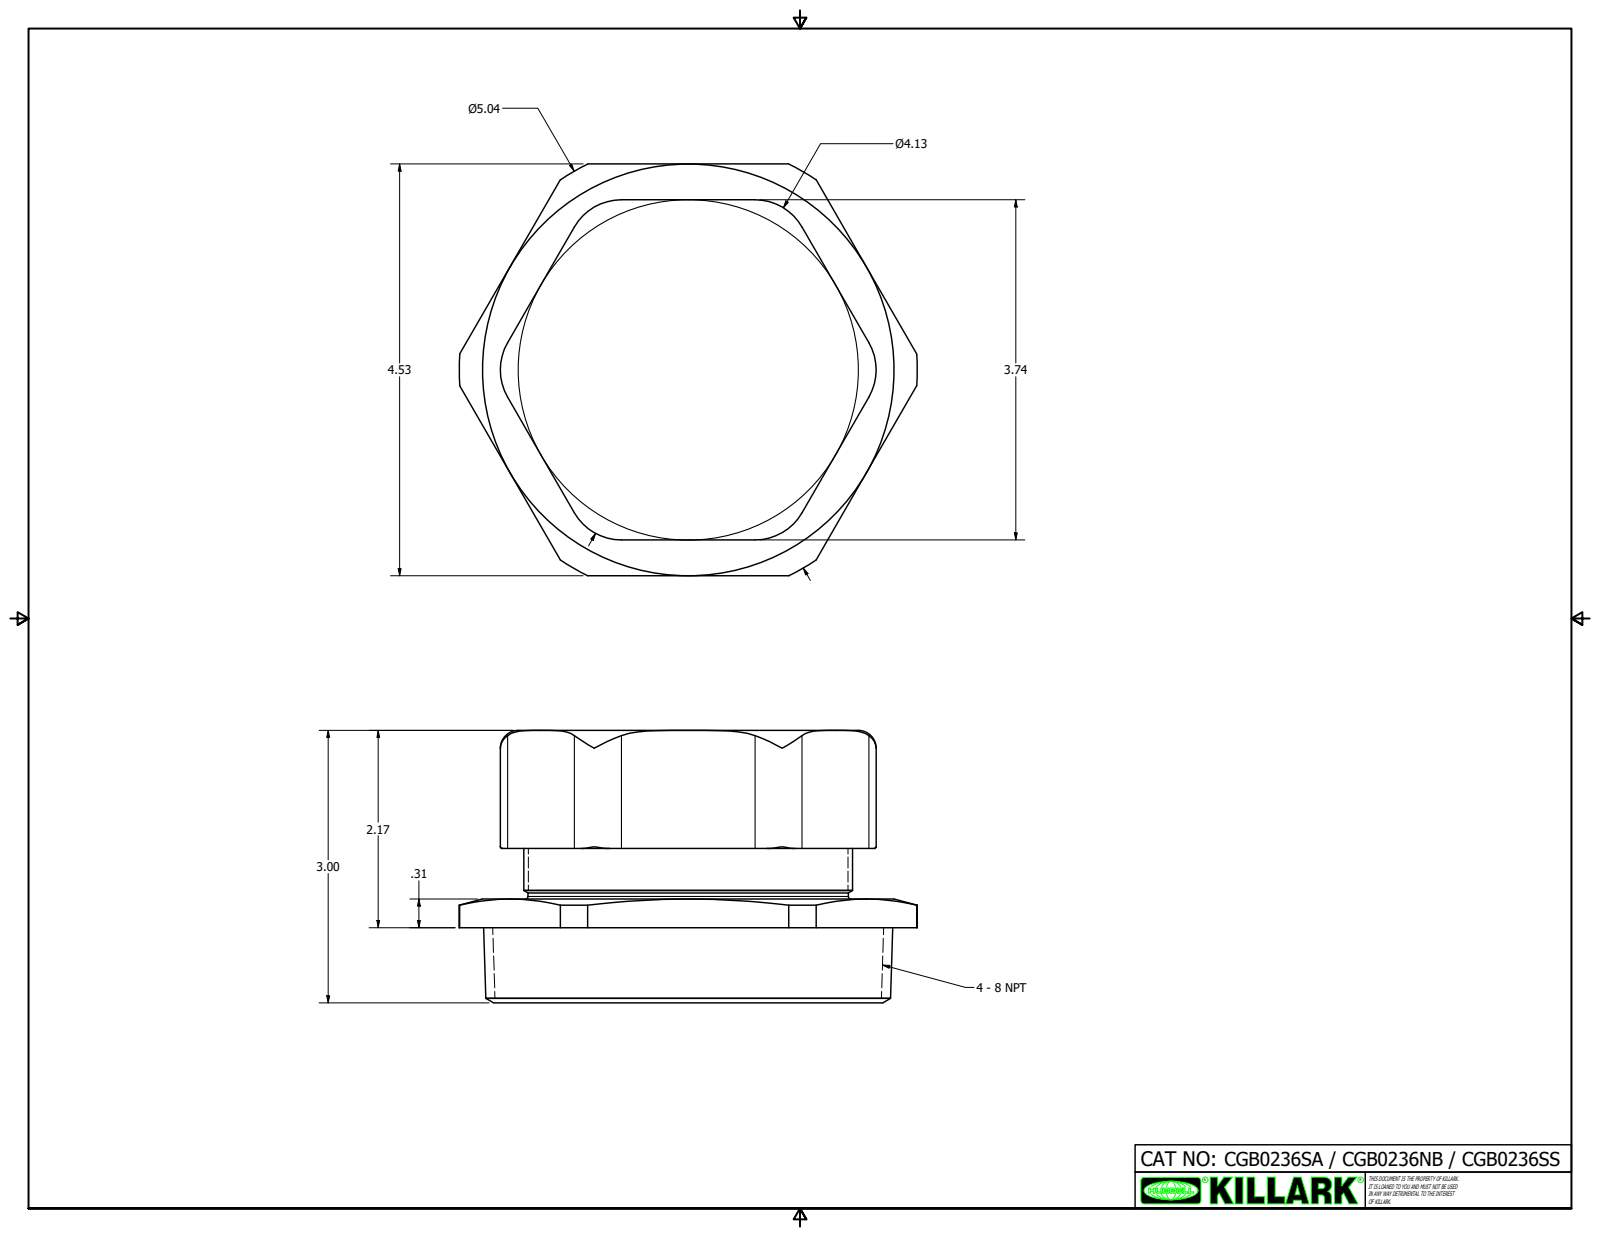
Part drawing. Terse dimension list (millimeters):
name: CGB0236
written by: Autodesk Inventor 2020 (AUTOMOTIVE_DESIGN)
unit: mm
bodies: 1 solid, 53 faces (17 planar, 14 cylindrical, 22 other)
size: 128 × 115 × 76.1
volume: 650 900 mm³; area: 49 640 mm²
bosses: 1× ⌀91.8, 1× ⌀89.5
rounds: 6× R15.2, 1× R64
face distances: 76.1, 29, 47.1, 95, 10, 105, 115, 21, 8, 55.1
